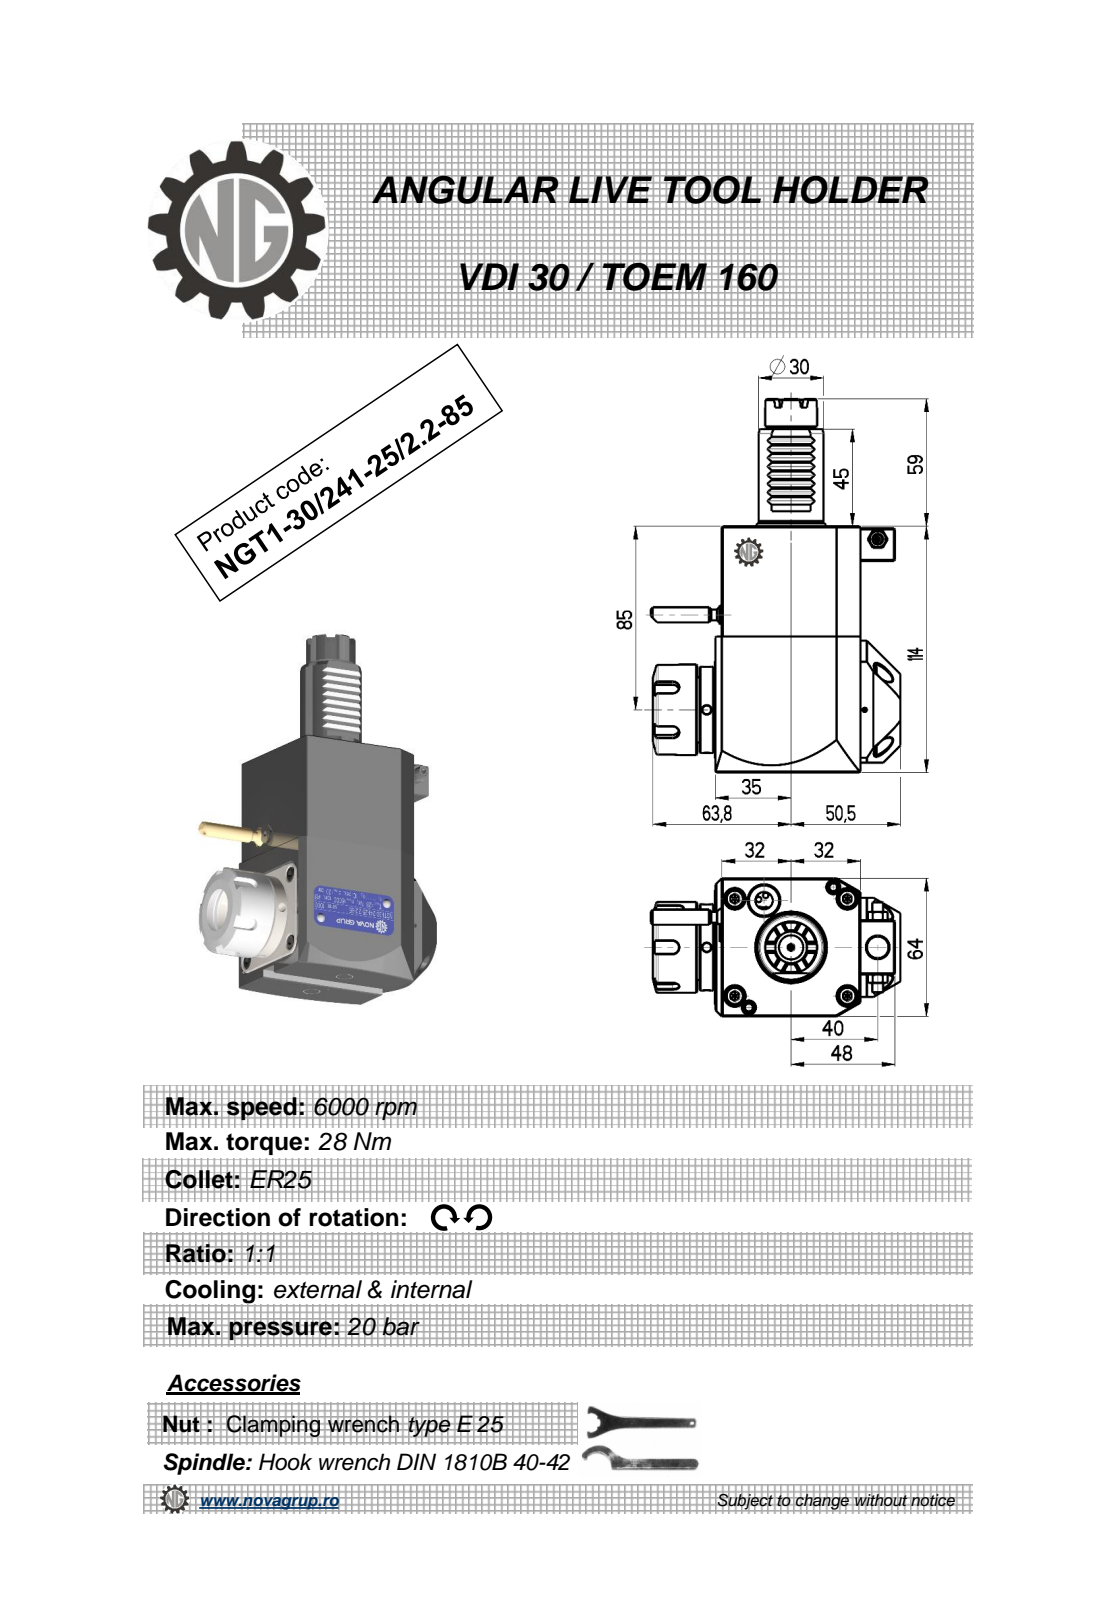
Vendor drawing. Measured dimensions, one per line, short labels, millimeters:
name: NGT1_30_241_25_2_2_85
written by: PRO/ENGINEER BY PARAMETRIC TECHNOLOGY CORPORATION, 2010280 (CONFIG_CONTROL_DESIGN)
unit: mm
bodies: 1 solid, 445 faces (208 planar, 86 cylindrical, 151 other)
size: 173 × 115.38 × 65.6
volume: 576 471 mm³; area: 54 117 mm²
holes: 2× ⌀4, 1× ⌀2.5, 1× ⌀3, 1× ⌀4.2, 1× ⌀9.5, 1× ⌀10, 1× ⌀20.3
bosses: 2× ⌀8.96, 2× ⌀5, 1× ⌀42, 1× ⌀40, 1× ⌀33, 1× ⌀30, 1× ⌀24, 1× ⌀17.7
rounds: 12× R0.26, 8× R0.3, 5× R3, 2× R160, 1× R32
face distances: 64, 114, 3.2, 67.2, 67, 3, 0.5, 85.7, 85.5, 82.5
hole spacings: 35.39, 46.17, 76.5, 78.95, 111.69
